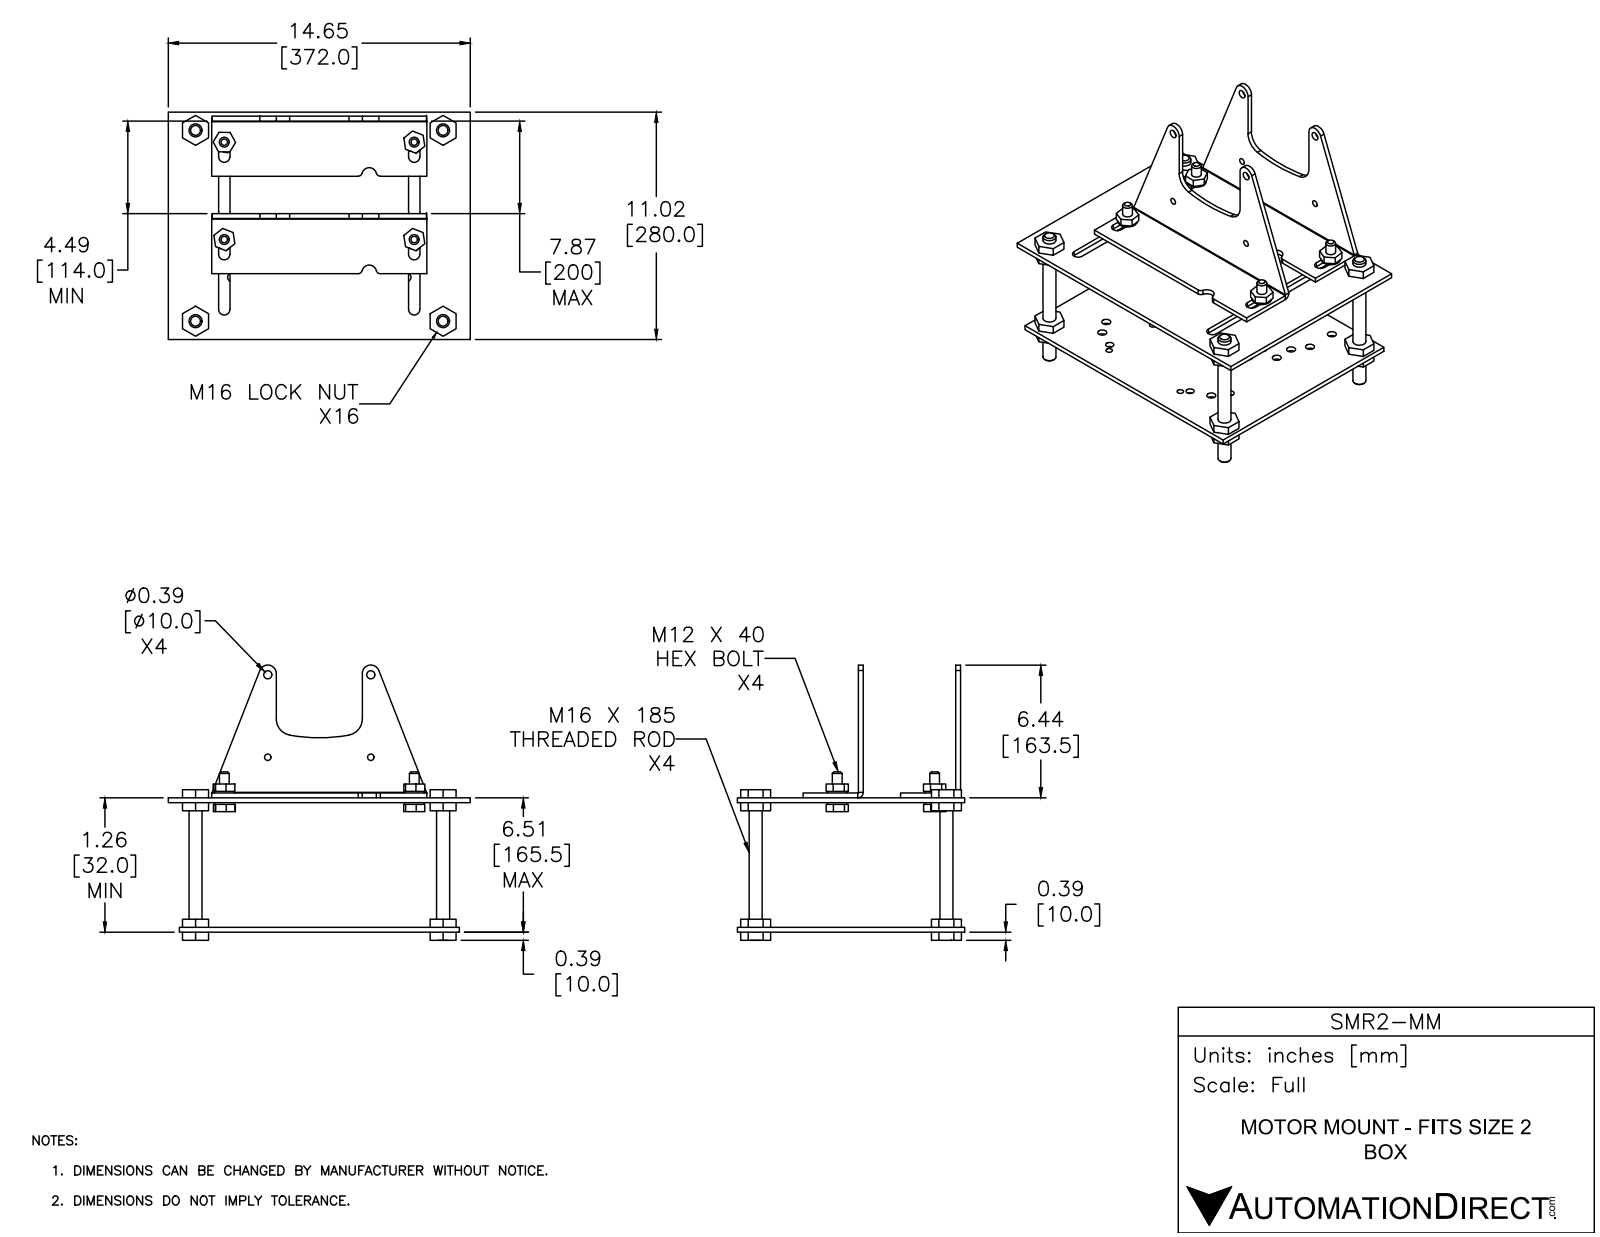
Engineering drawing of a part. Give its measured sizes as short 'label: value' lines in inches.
name: SMR2-MM
written by: SolidWorks 2016 (AUTOMOTIVE_DESIGN)
unit: in
bodies: 40 solids, 504 faces (272 planar, 204 cylindrical, 28 other)
size: 14.646 × 13.079 × 11.024
volume: 119.1 in³; area: 1 089 in²
holes: 12× ⌀0.433, 8× ⌀0.394, 6× ⌀0.315, 4× ⌀0.472, 4× ⌀0.63, 4× ⌀0.669
bosses: 4× ⌀0.945
rounds: 12× R0.276, 4× R0.197, 2× R0.029, 2× R0.265, 2× R0.354, 2× R0.413, 2× R0.787, 1× R7.992
face distances: 0.236, 4.633, 4.87, 4.397, 4.724, 5.106, 0.472, 4.961, 4.488, 0.63
hole spacings: 5.512, 0.984, 1.365, 5, 6.565, 7.48, 8.465, 0.474
